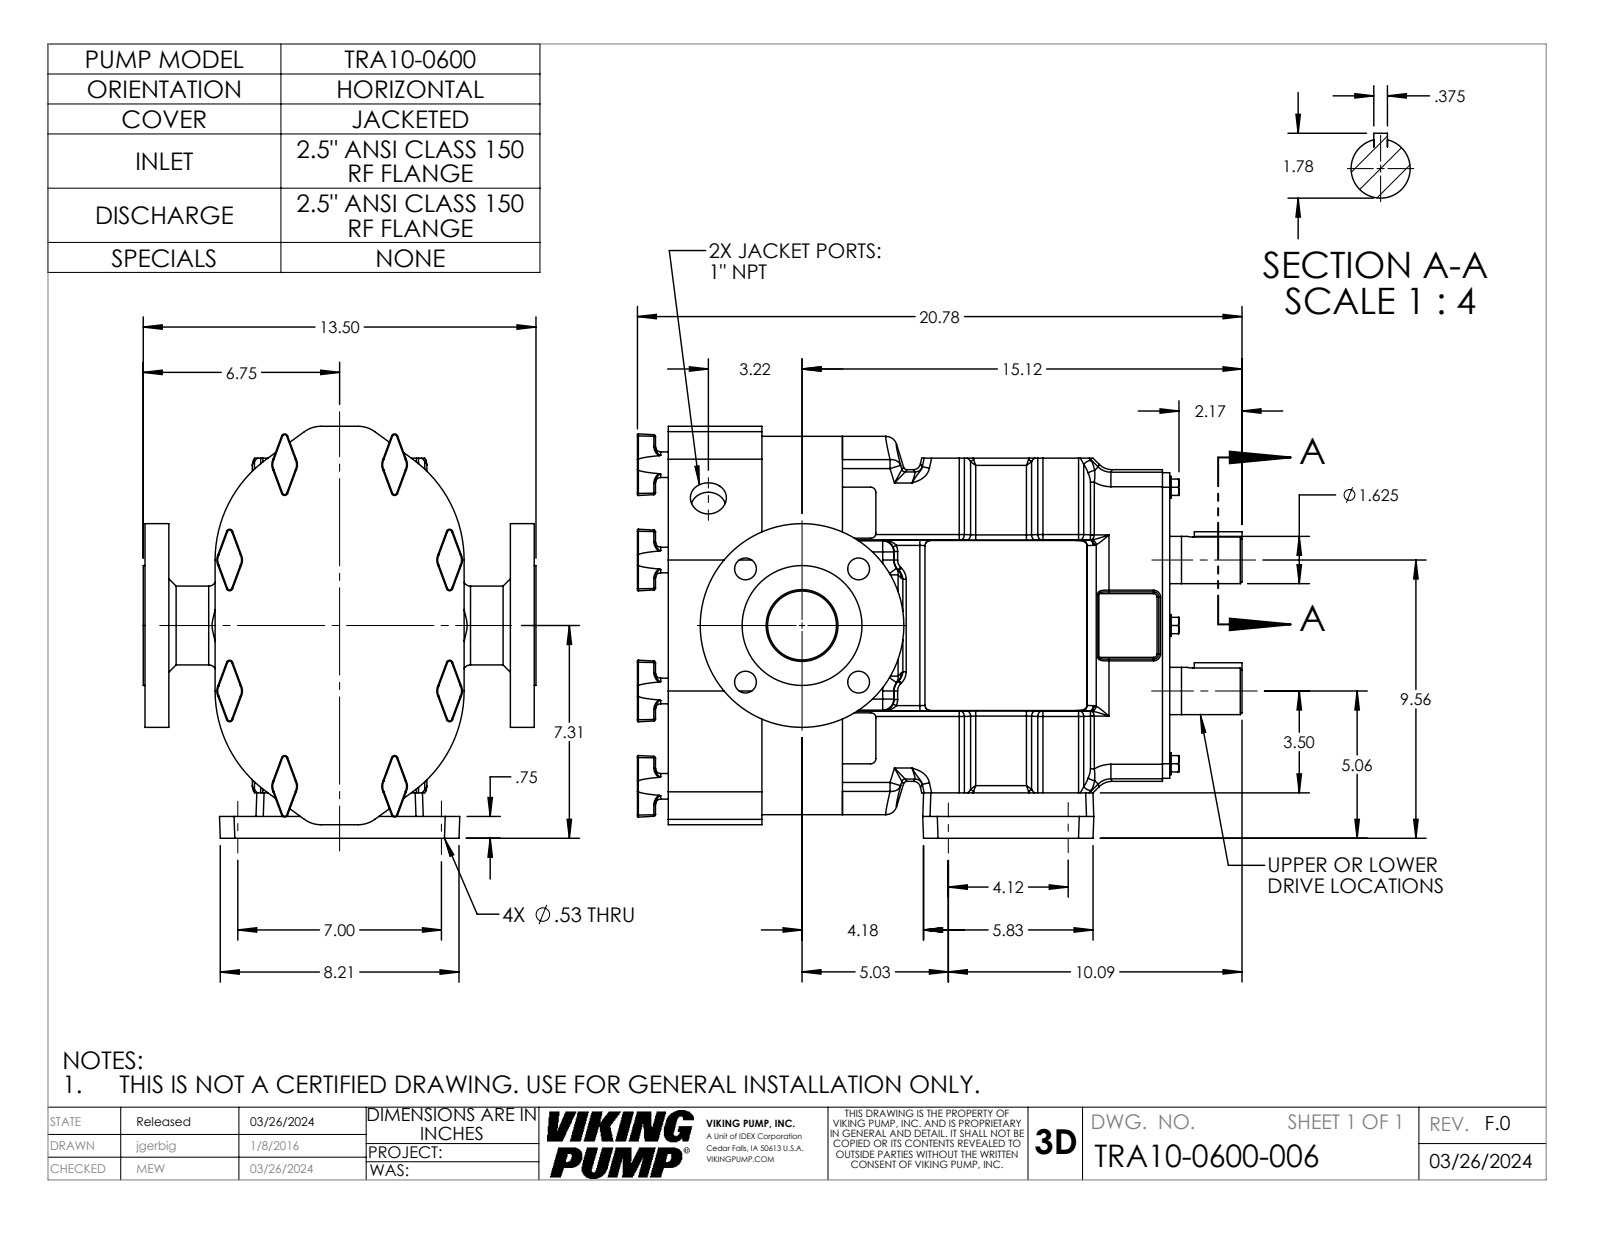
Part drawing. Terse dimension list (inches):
name: TRA10-0600-GEARBOX-H; TRA10-0600-COVER-JACKET; TRA10-0600-006; 0600FLG150-25 (+1 more)
written by: SolidWorks 2022 (AUTOMOTIVE_DESIGN)
unit: in
bodies: 5 solids, 1052 faces (286 planar, 386 cylindrical, 380 other)
size: 20.781 × 14.155 × 13.5
volume: 1 441 in³; area: 1 606 in²
holes: 4× ⌀0.531, 4× ⌀0.75, 1× ⌀2.368, 1× ⌀2.47
bosses: 8× ⌀0.88, 6× ⌀0.75, 2× ⌀1.624, 1× ⌀7, 1× ⌀4.12, 1× ⌀2.708
rounds: 44× R0.18, 43× R0.06, 32× R0.03, 30× R0.25, 28× R0.38, 24× R0.12, 20× R0.5, 12× R0.375
face distances: 2.769, 3.218, 5.987, 0.5, 11.25, 0.36, 2.37, 9.37, 17.237, 14.019
hole spacings: 2.75, 3.889, 4.12, 5.5, 7, 8.122
